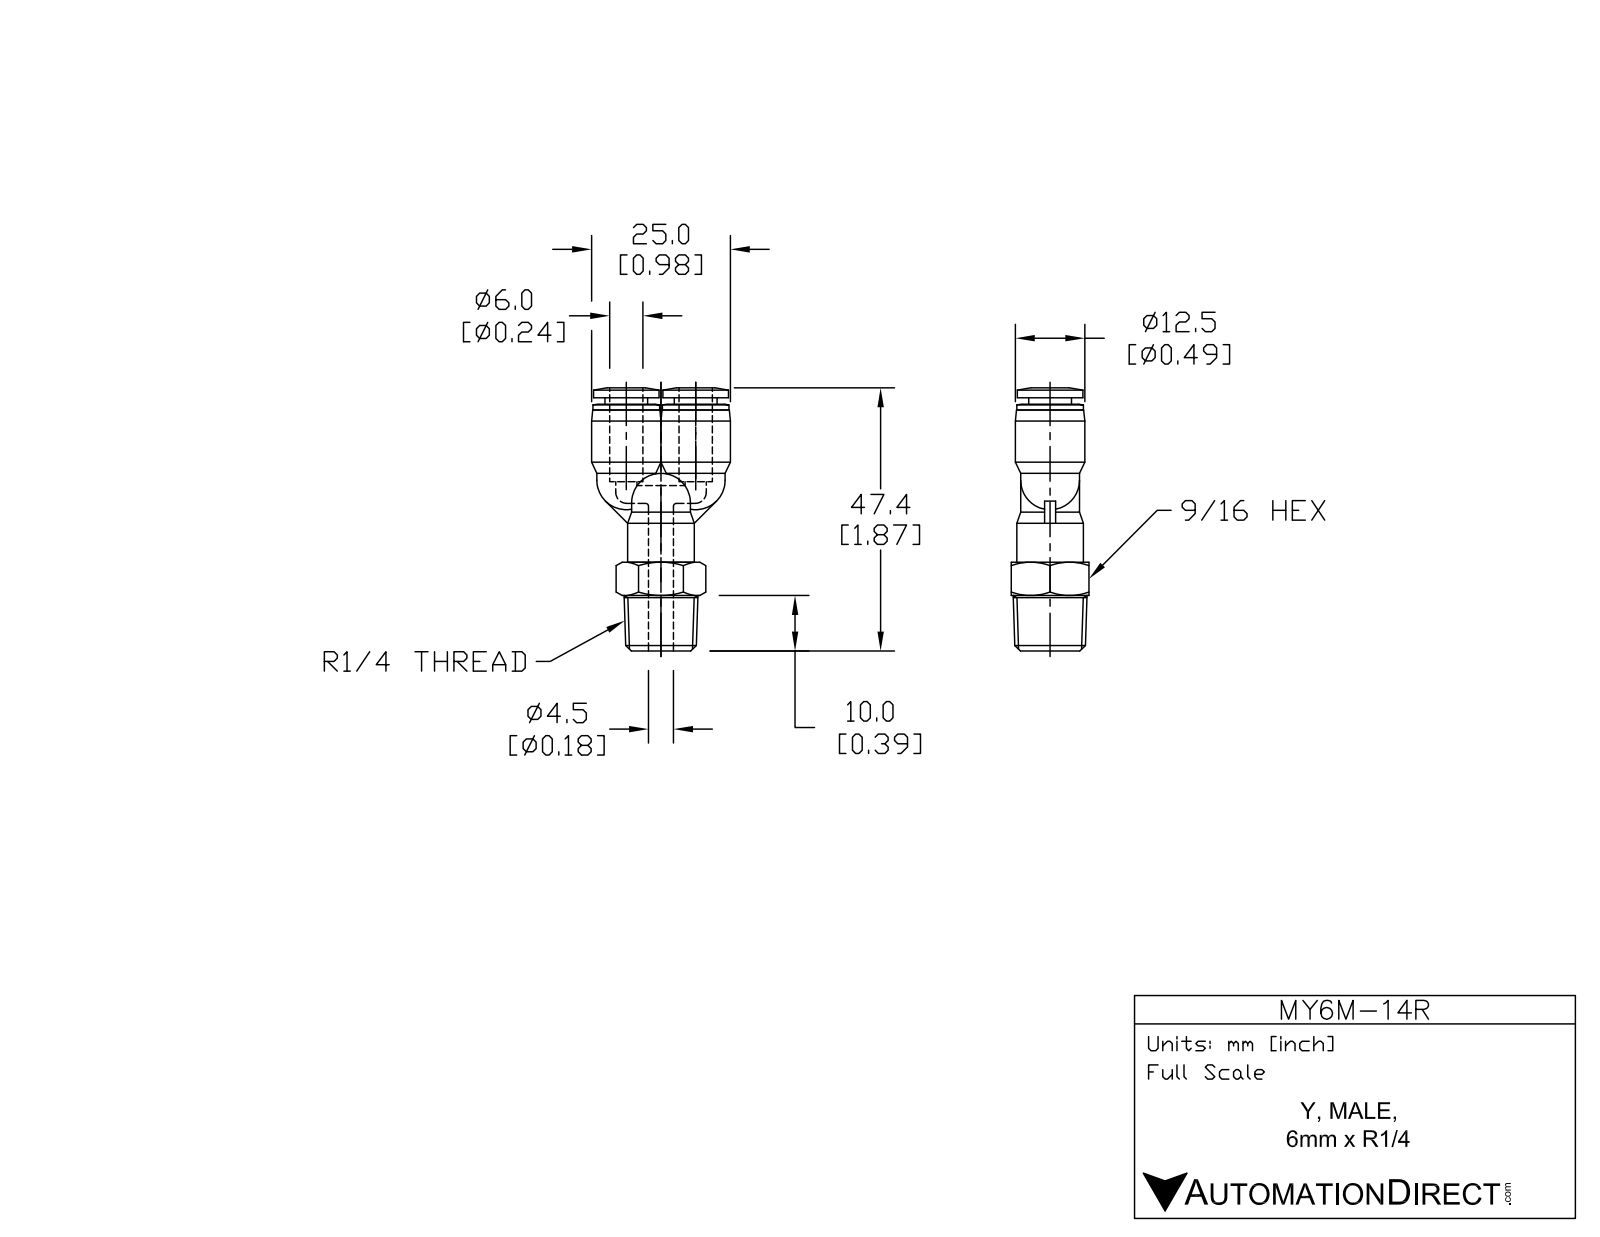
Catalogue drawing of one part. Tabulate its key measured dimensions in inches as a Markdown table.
| quantity | value |
| --- | --- |
| part name | MY6M-14R |
| STEP written by | SolidWorks 2015 (AUTOMOTIVE_DESIGN) |
| units | inches |
| bodies | 1 solid, 109 faces (24 planar, 37 cylindrical, 48 other) |
| overall size | 1.785 × 0.827 × 0.551 |
| volume | 0.317 in³ |
| surface area | 5.415 in² |
| round holes (diameter × count) | 0.118 × 4, 0.169 × 2 |
| round bosses / shafts (diameter × count) | 0.394 × 3, 0.354 × 3, 0.413 × 2, 0.382 × 2, 0.22 × 2 |
| main face-to-face distances | 0.551, 1.719, 0.591, 1.128, 1.675, 1.085, 0.043, 0.236, 0.315, 0.394 |
| hole center spacings | 0.207, 0.413 |
